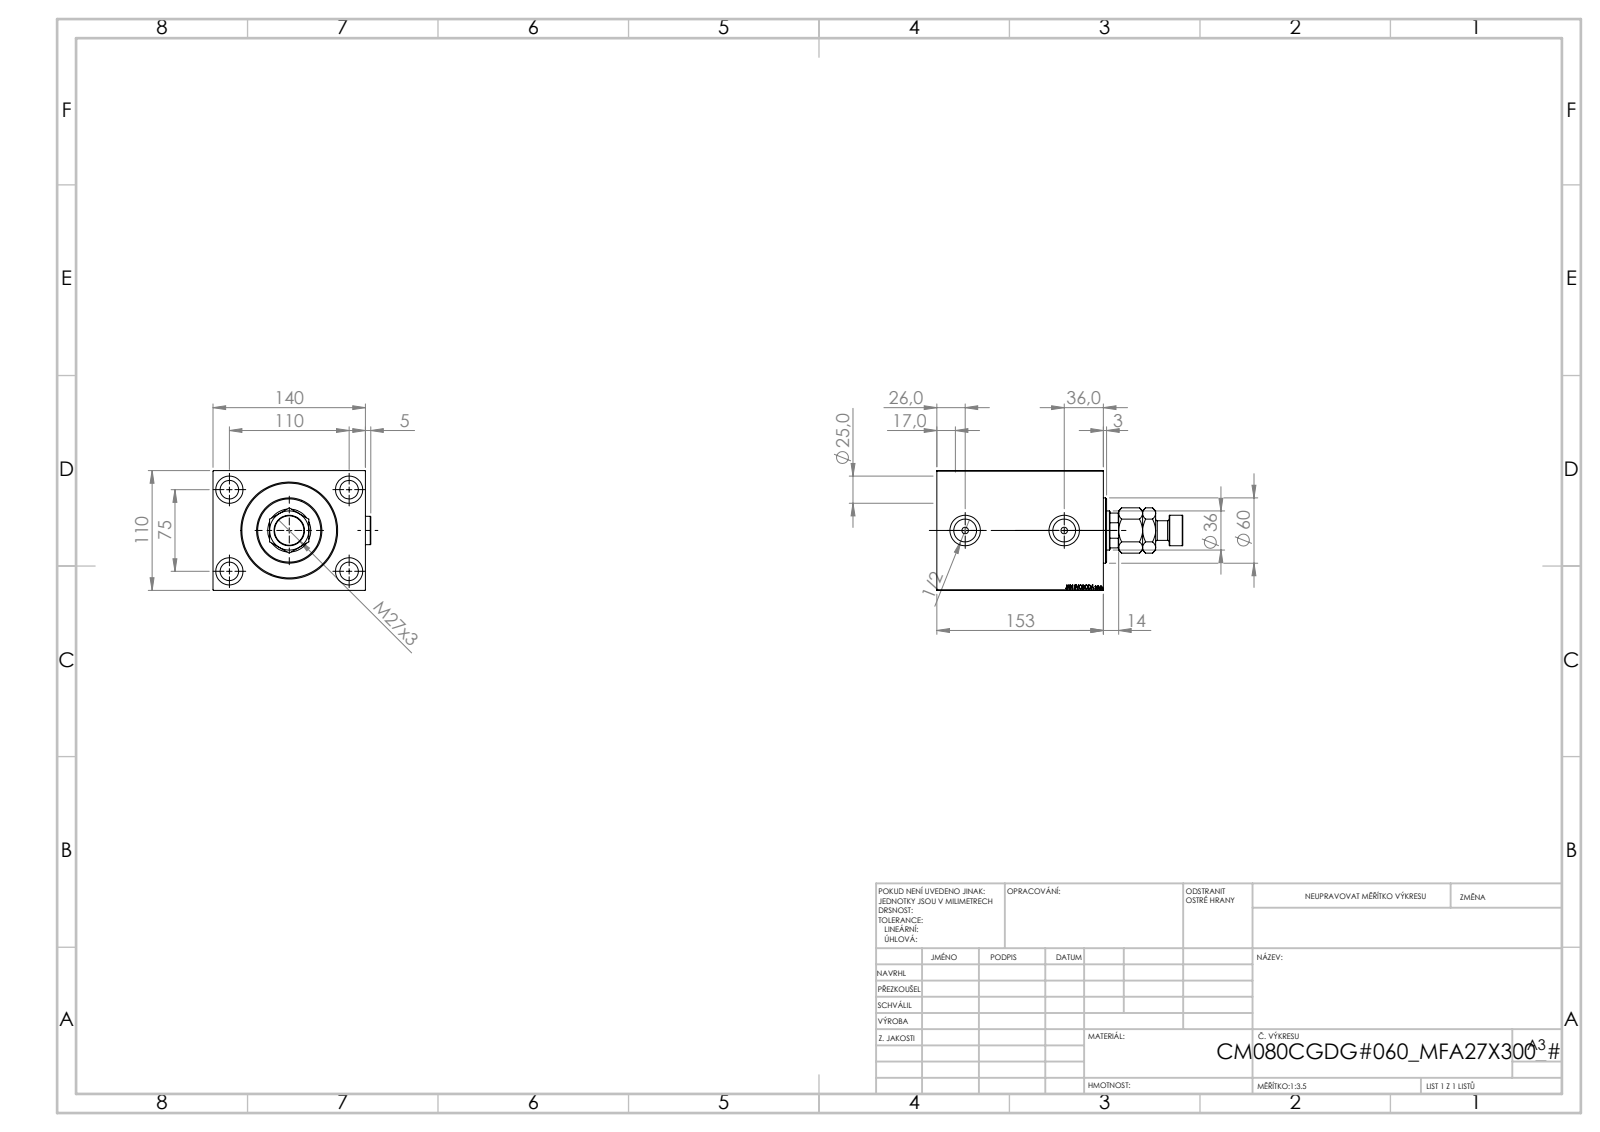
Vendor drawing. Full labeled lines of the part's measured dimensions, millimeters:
Part name (STEP PRODUCT): V450CM_C_VCP; Zatka_OIL_PORT; V450CM_VC_B; MFA (+1 more)
STEP written by: SolidWorks 2019 (CONFIG_CONTROL_DESIGN)
Units: millimetres
Bodies: 6 solids, 971 faces (459 planar, 82 cylindrical, 430 other)
Overall size (bounding box): 226 × 144.9 × 110
Volume: 1 975 000 mm³ · Surface area: 244 177 mm²
Round holes (diameter × count): ⌀17 ×4, ⌀25 ×4, ⌀6 ×2, ⌀20.96 ×2, ⌀28 ×2, ⌀25.5 ×1, ⌀36 ×1, ⌀39.5 ×1, ⌀80 ×1, ⌀82 ×1, ⌀87 ×1
Round bosses / shafts (diameter × count): ⌀26 ×2, ⌀60 ×1, ⌀28 ×1, ⌀18 ×1
Partial cylindrical surfaces — rounded edges, fillets, slot ends (radius × count): R17.5 ×1
Main face-to-face distances: 110, 140, 153, 132, 21, 14, 139, 118, 74, 60
Hole centre spacings: 66.57, 75, 110, 133.14, 91
